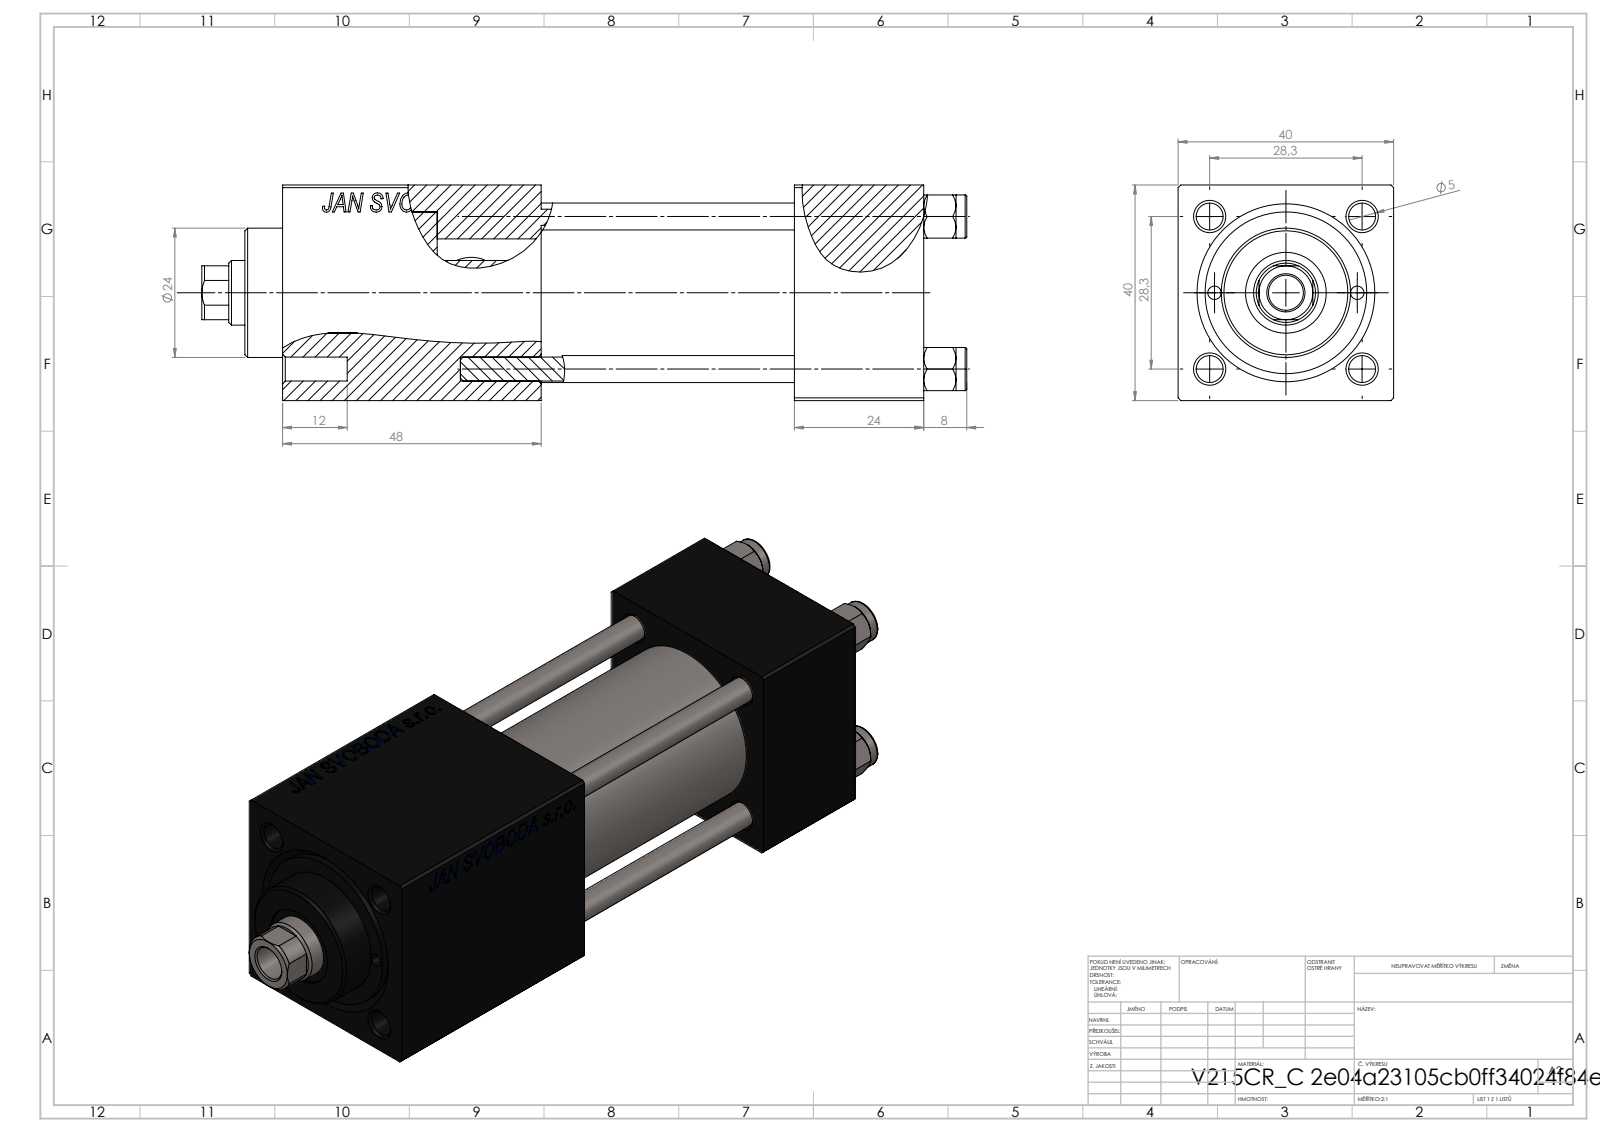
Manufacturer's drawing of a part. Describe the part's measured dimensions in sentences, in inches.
The part is named "V215CR_VCP_C; V215CR_C_TYCINKA; V215_VC_A; NUT_M5_C (+1 more)". Its 3-D file was written by "SolidWorks 2019 (CONFIG_CONTROL_DESIGN)". It is 11 solids with 1153 faces: 527 planar, 90 cylindrical and 536 other. Overall it measures 5.591 by 1.575 by 1.575 inches. Its volume is 8.686 cubic inches and its surface area 84.51 square inches. Round holes: 4 of diameter 0.197, 3 of diameter 0.787, 2 of diameter 0.098, 2 of diameter 0.276, 2 of diameter 0.518, 1 of diameter 0.256, 1 of diameter 0.472, 1 of diameter 0.591, 1 of diameter 0.984, 1 of diameter 1.181. Round bosses or shafts: 4 of diameter 0.315, 1 of diameter 1.22, 1 of diameter 0.945. Partial cylindrical surfaces (rounded edges, fillets, slot ends): 1 of radius 0.217. The main face-to-face distances are 1.575, 0.945, 3.555, 2.61, 1.89, 2.795, 1.85, 0.76, 4.685, 3.74. The hole center spacings are 0.558, 0.788, 1.114, 1.214, 0.522, 1.576, 1.043, 2.835.
